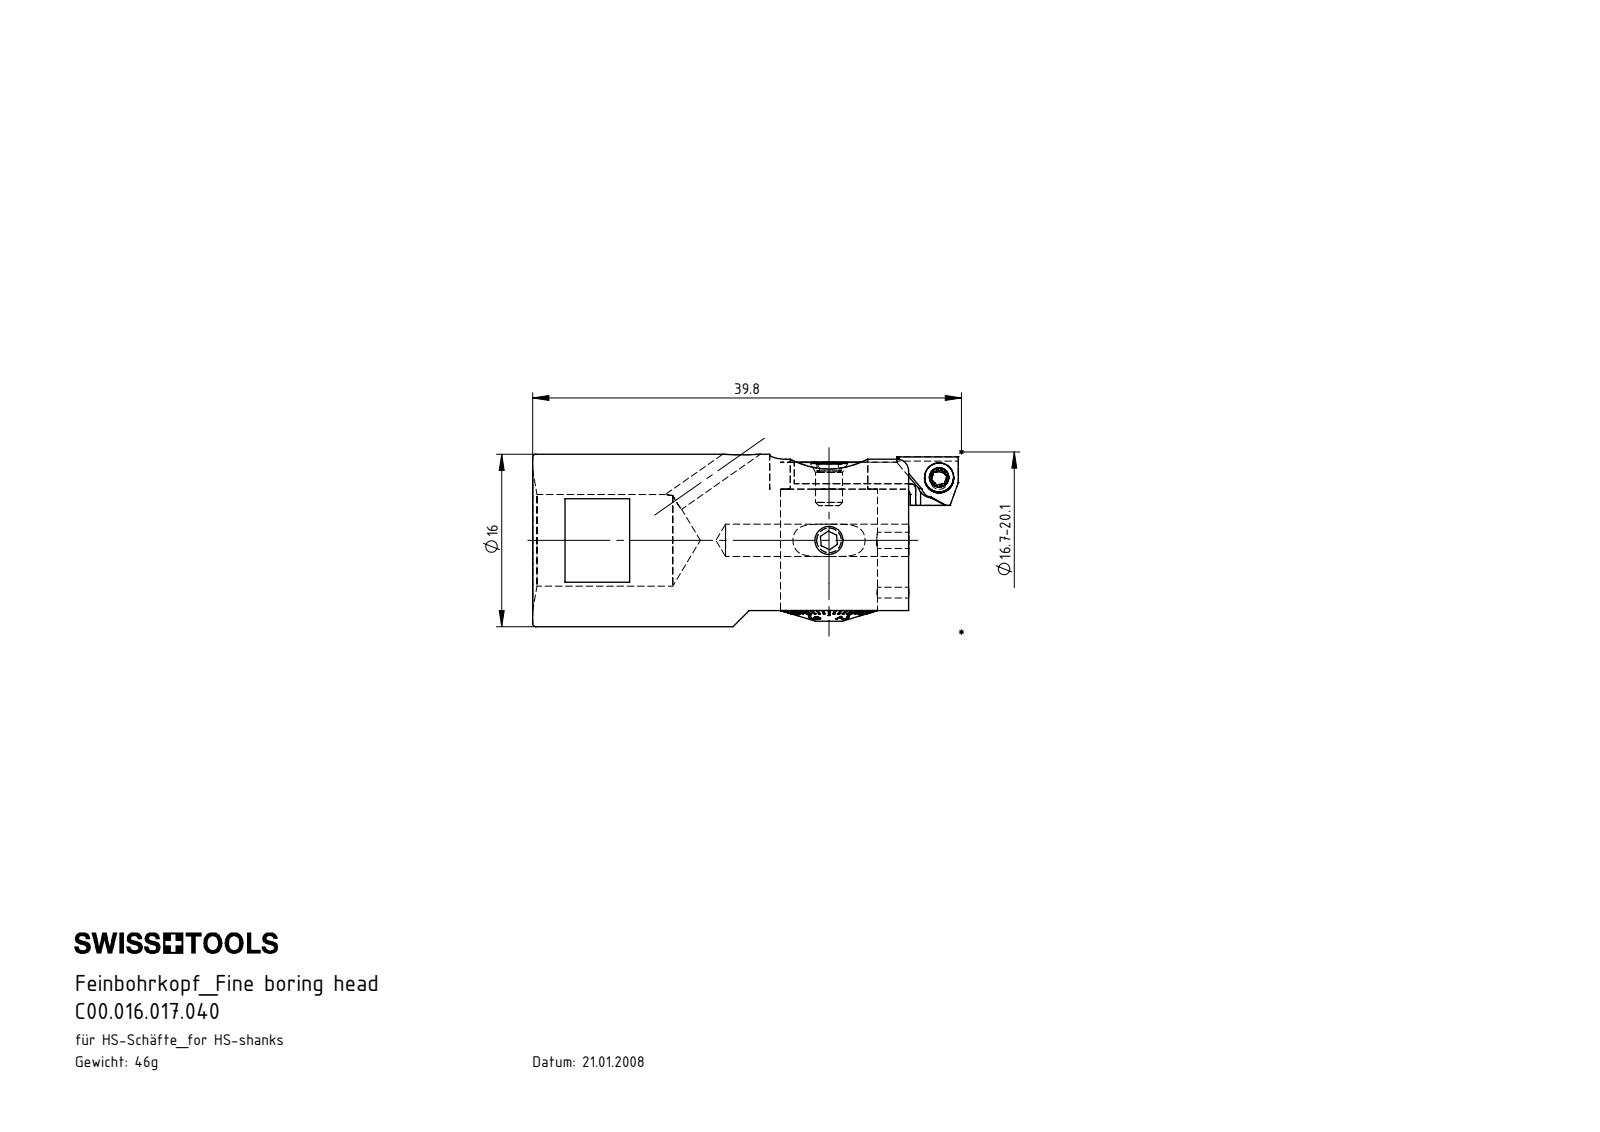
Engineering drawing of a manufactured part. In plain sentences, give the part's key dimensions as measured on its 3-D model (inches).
The part is named "HS0.F16.K11.040; F14-WWA.001.004; WWA-ER2.001.004_A; WWA-U02.001.002 (+8 more)". Its 3-D file was written by "SolidWorks 2012 (CONFIG_CONTROL_DESIGN)". It is 16 solids with 697 faces: 409 planar, 149 cylindrical and 139 other. Overall it measures 1.565 by 0.636 by 0.63 inches. Its volume is 0.362 cubic inches and its surface area 7.562 square inches. Round holes: 2 of diameter 0.059, 2 of diameter 0.079, 2 of diameter 0.091, 1 of diameter 0.039, 1 of diameter 0.063, 1 of diameter 0.106, 1 of diameter 0.118, 1 of diameter 0.128, 1 of diameter 0.238, 1 of diameter 0.244, 1 of diameter 0.335. Round bosses or shafts: 2 of diameter 0.118, 1 of diameter 0.63, 1 of diameter 0.354, 1 of diameter 0.309, 1 of diameter 0.232, 1 of diameter 0.23, 1 of diameter 0.22, 1 of diameter 0.156. Partial cylindrical surfaces (rounded edges, fillets, slot ends): 12 of radius 0.007, 12 of radius 0.013, 6 of radius 0.009, 6 of radius 0.018, 3 of radius 0.012, 2 of radius 0.028, 2 of radius 0.039, 2 of radius 0.049. The main face-to-face distances are 0.098, 0.443, 0.382, 0.169, 0.344, 0.083, 0.427, 0.016, 0.213, 1.374. The hole center spacings are 0.026, 0.177, 0.191, 0.261.
